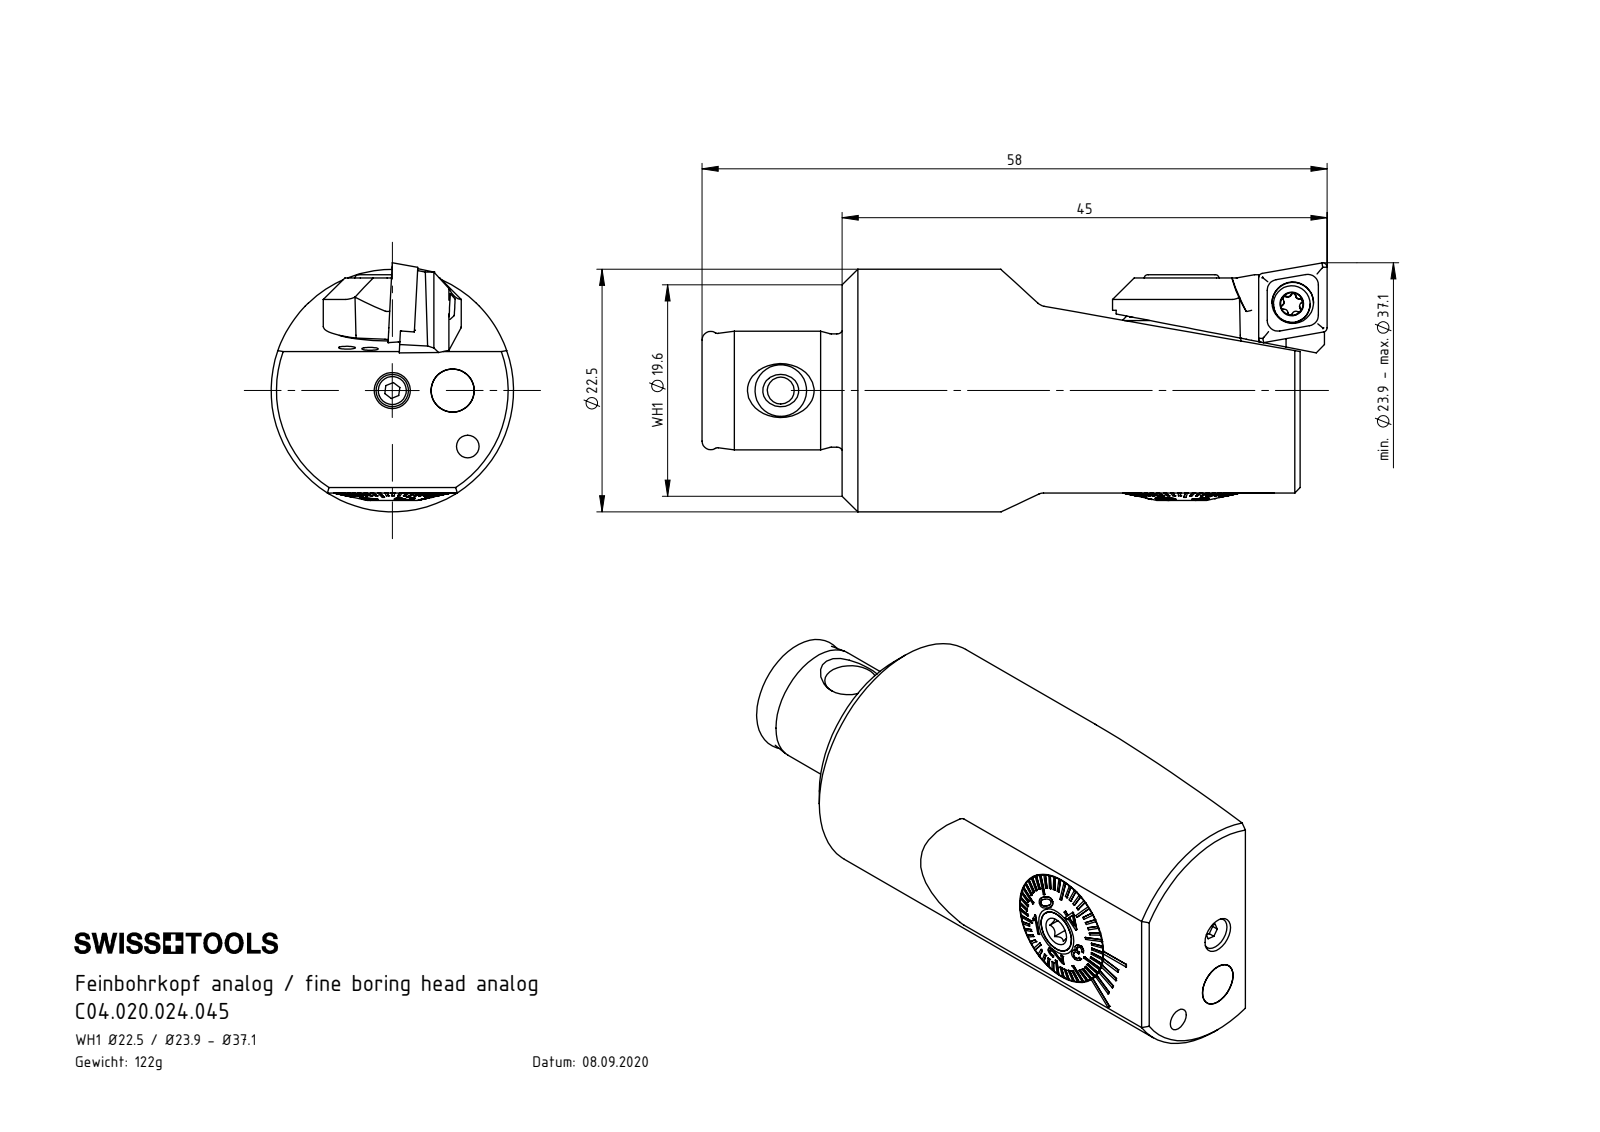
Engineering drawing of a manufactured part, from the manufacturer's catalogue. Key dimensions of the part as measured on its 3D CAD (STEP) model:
Part name (STEP PRODUCT): F20-BG1.AA4.011_verstellbar; F20-BG1.AA3.011_A_Standart; F20-BG2.008.009_A; WH1-F20.AA3.045_A_Khlung neu (+8 more)
STEP written by: SolidWorks 2017 (CONFIG_CONTROL_DESIGN)
Units: millimetres
Bodies: 13 solids, 644 faces (285 planar, 107 cylindrical, 252 other)
Overall size (bounding box): 55.5 × 22.5 × 22.5
Volume: 15 121 mm³ · Surface area: 8 122 mm²
Round holes (diameter × count): ⌀2.1 ×4, ⌀1.5 ×2, ⌀3 ×2, ⌀3.3 ×2, ⌀1.08 ×1, ⌀1.9 ×1, ⌀2.5 ×1, ⌀4 ×1, ⌀4.2 ×1, ⌀4.5 ×1, ⌀5.4 ×1, ⌀6.2 ×1
Round bosses / shafts (diameter × count): ⌀11 ×2, ⌀4 ×2, ⌀3.95 ×2, ⌀22.5 ×1, ⌀10.98 ×1, ⌀10.85 ×1, ⌀10.5 ×1, ⌀8.65 ×1
Partial cylindrical surfaces — rounded edges, fillets, slot ends (radius × count): R0.3 ×2, R1.25 ×2, R2 ×2
Main face-to-face distances: 42.5, 3.7, 1.5, 0.8, 2.9, 2.8, 1.4, 12.6, 15.5, 16.3
Hole centre spacings: 5.38, 5.6, 8.71, 37.2
